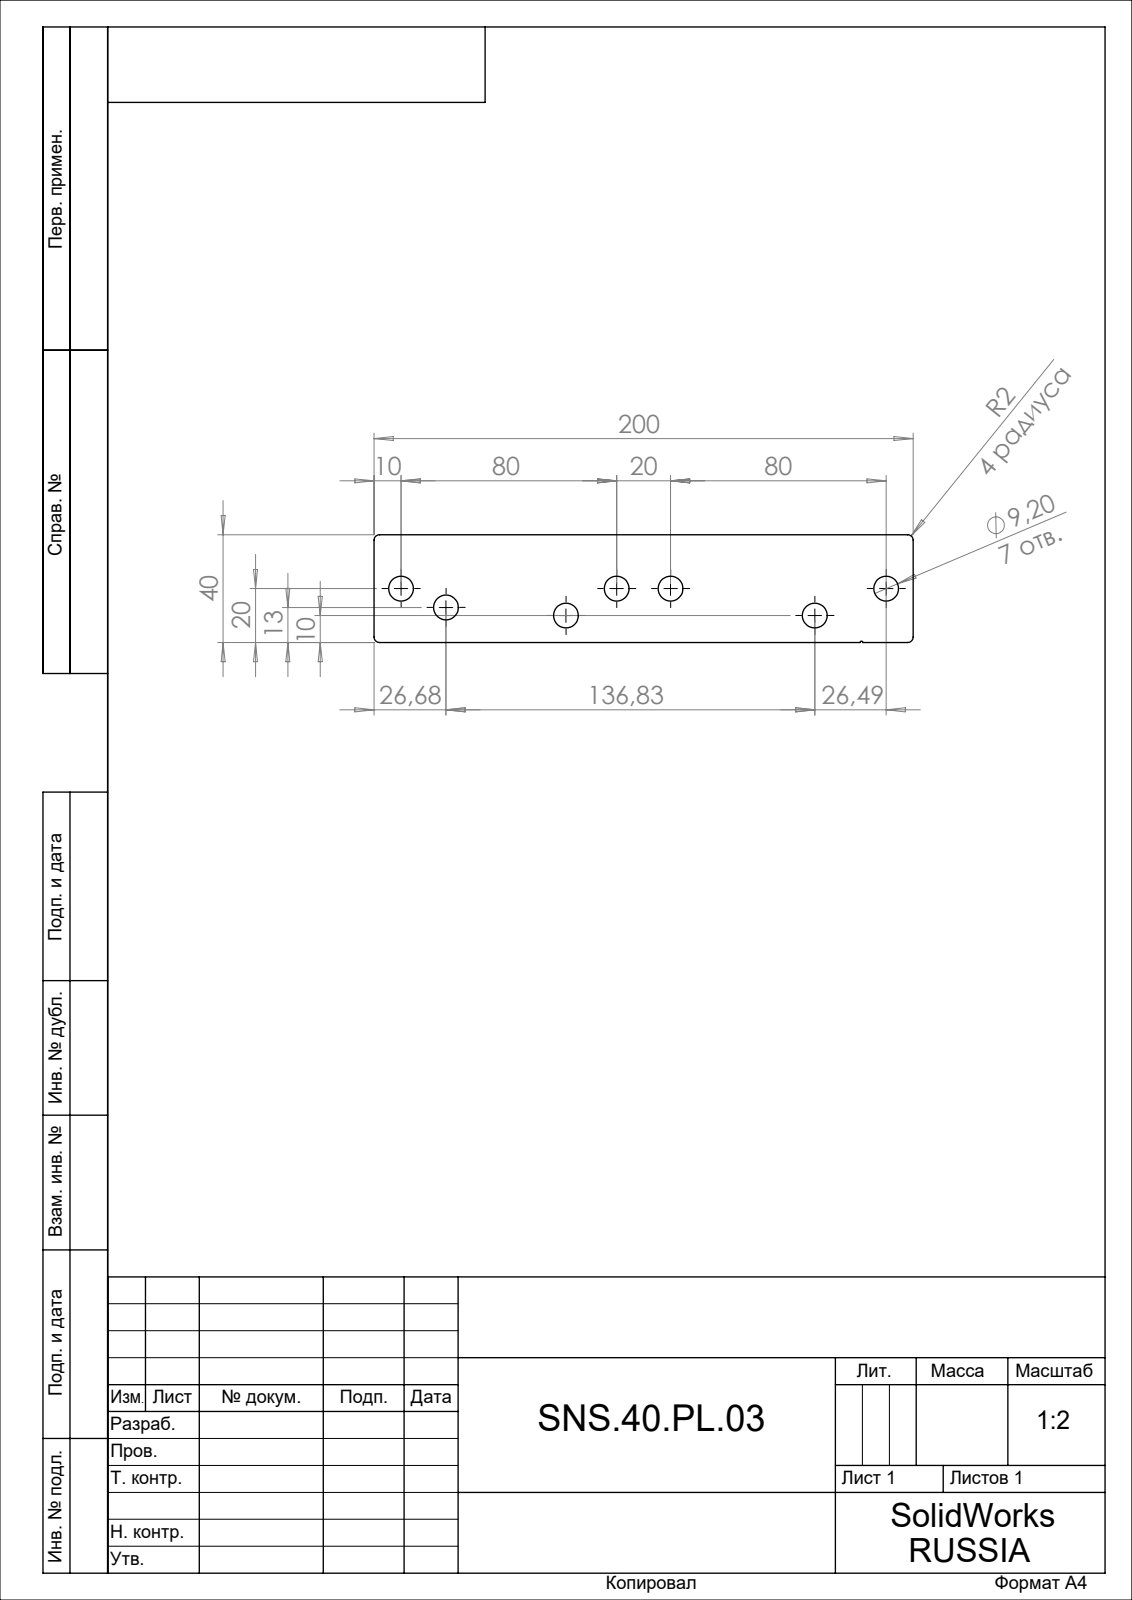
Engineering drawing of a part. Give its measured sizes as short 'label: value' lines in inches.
written by: SolidWorks 2018 (AUTOMOTIVE_DESIGN)
unit: in
bodies: 1 solid, 26 faces (7 planar, 19 cylindrical, 0 other)
size: 7.874 × 1.575 × 0.197
volume: 2.298 in³; area: 28.61 in²
holes: 7× ⌀0.362
rounds: 4× R0.079, 1× R0.02
face distances: 0.197, 1.575, 7.874
hole spacings: 3.15, 3.937, 0.712, 0.787, 0.839, 1.115, 1.578, 1.756
